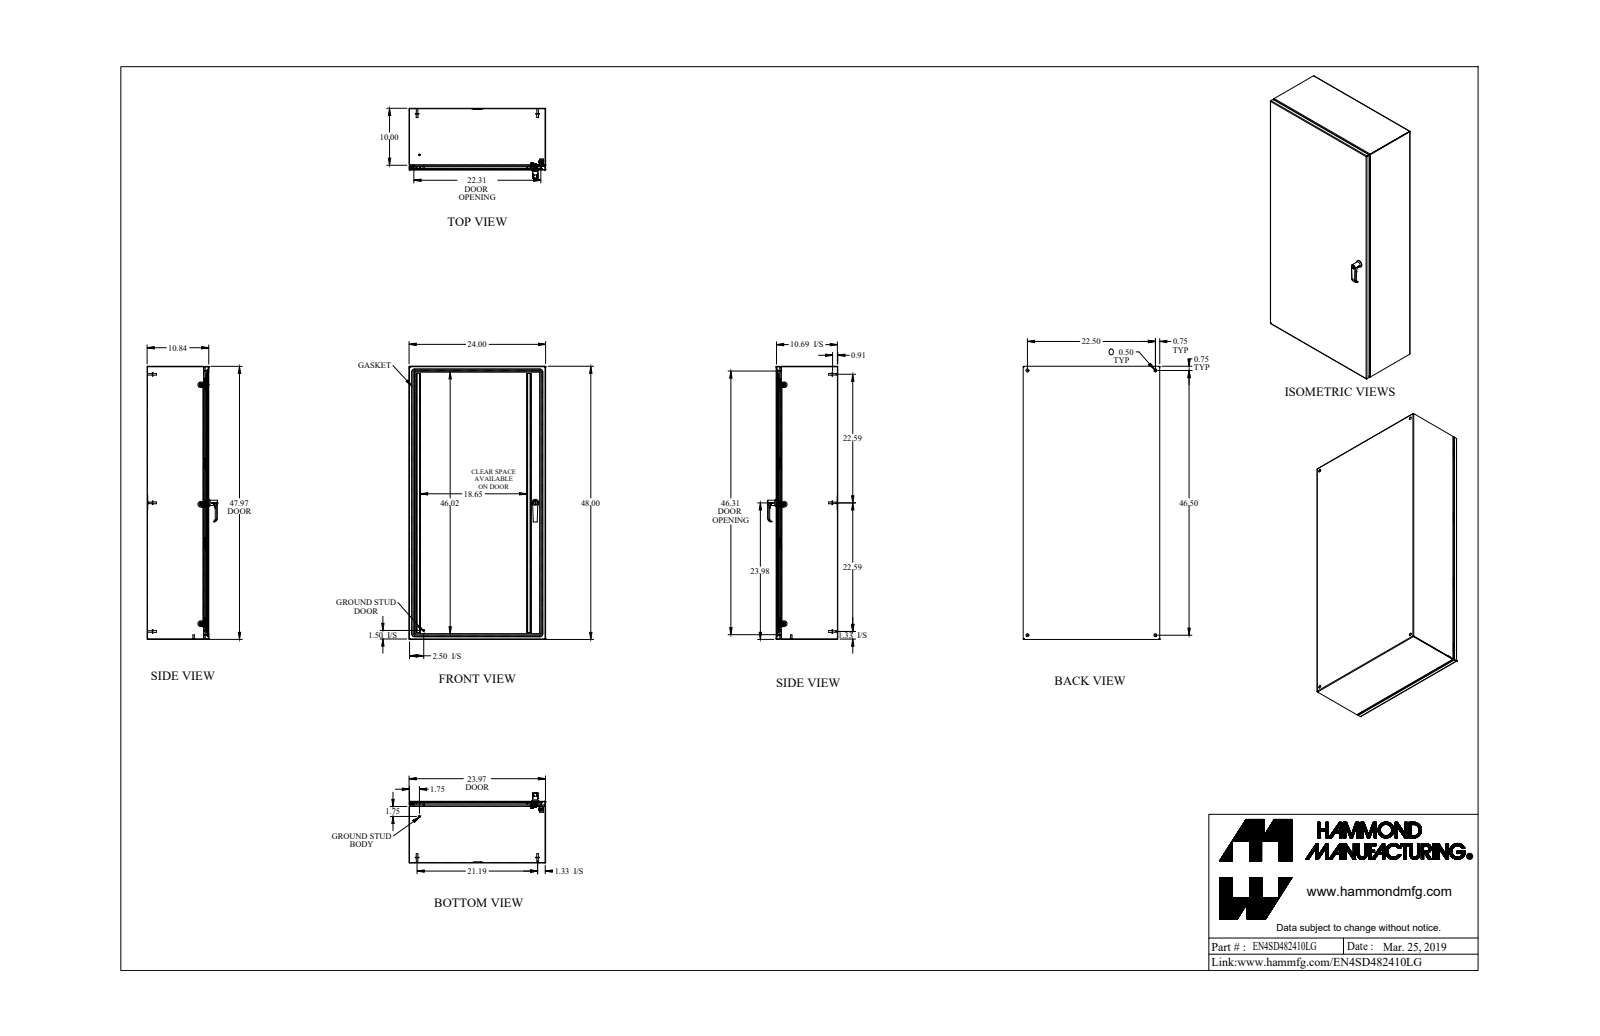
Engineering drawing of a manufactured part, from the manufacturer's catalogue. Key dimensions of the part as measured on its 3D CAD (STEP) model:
Part name (STEP PRODUCT): EN4SD482410LG
STEP written by: SolidWorks 2018 (AUTOMOTIVE_DESIGN)
Units: inches
Bodies: 53 solids, 1457 faces (632 planar, 538 cylindrical, 287 other)
Overall size (bounding box): 48 × 24 × 12.367
Volume: 319.5 in³ · Surface area: 8 869 in²
Round holes (diameter × count): ⌀0.176 ×6, ⌀0.5 ×4, ⌀0.196 ×3, ⌀0.25 ×3, ⌀0.265 ×3, ⌀0.413 ×3, ⌀0.256 ×2, ⌀0.313 ×2, ⌀0.394 ×2, ⌀0.172 ×1, ⌀0.24 ×1, ⌀0.242 ×1
Round bosses / shafts (diameter × count): ⌀0.25 ×7, ⌀0.625 ×6, ⌀0.375 ×6, ⌀0.313 ×6, ⌀0.27 ×6, ⌀0.156 ×6, ⌀1 ×3, ⌀0.63 ×2
Partial cylindrical surfaces — rounded edges, fillets, slot ends (radius × count): R0.036 ×20, R0.108 ×20, R0.03 ×15, R0.043 ×12, R0.081 ×12, R0.006 ×8, R0.04 ×8, R0.062 ×8
Main face-to-face distances: 0.072, 10.765, 10.693, 10.837, 23.928, 23.856, 24, 0.072, 47.928, 47.928
Hole centre spacings: 0.787, 20.982, 21, 21.546, 22.5, 41.969, 46.5, 51.657
